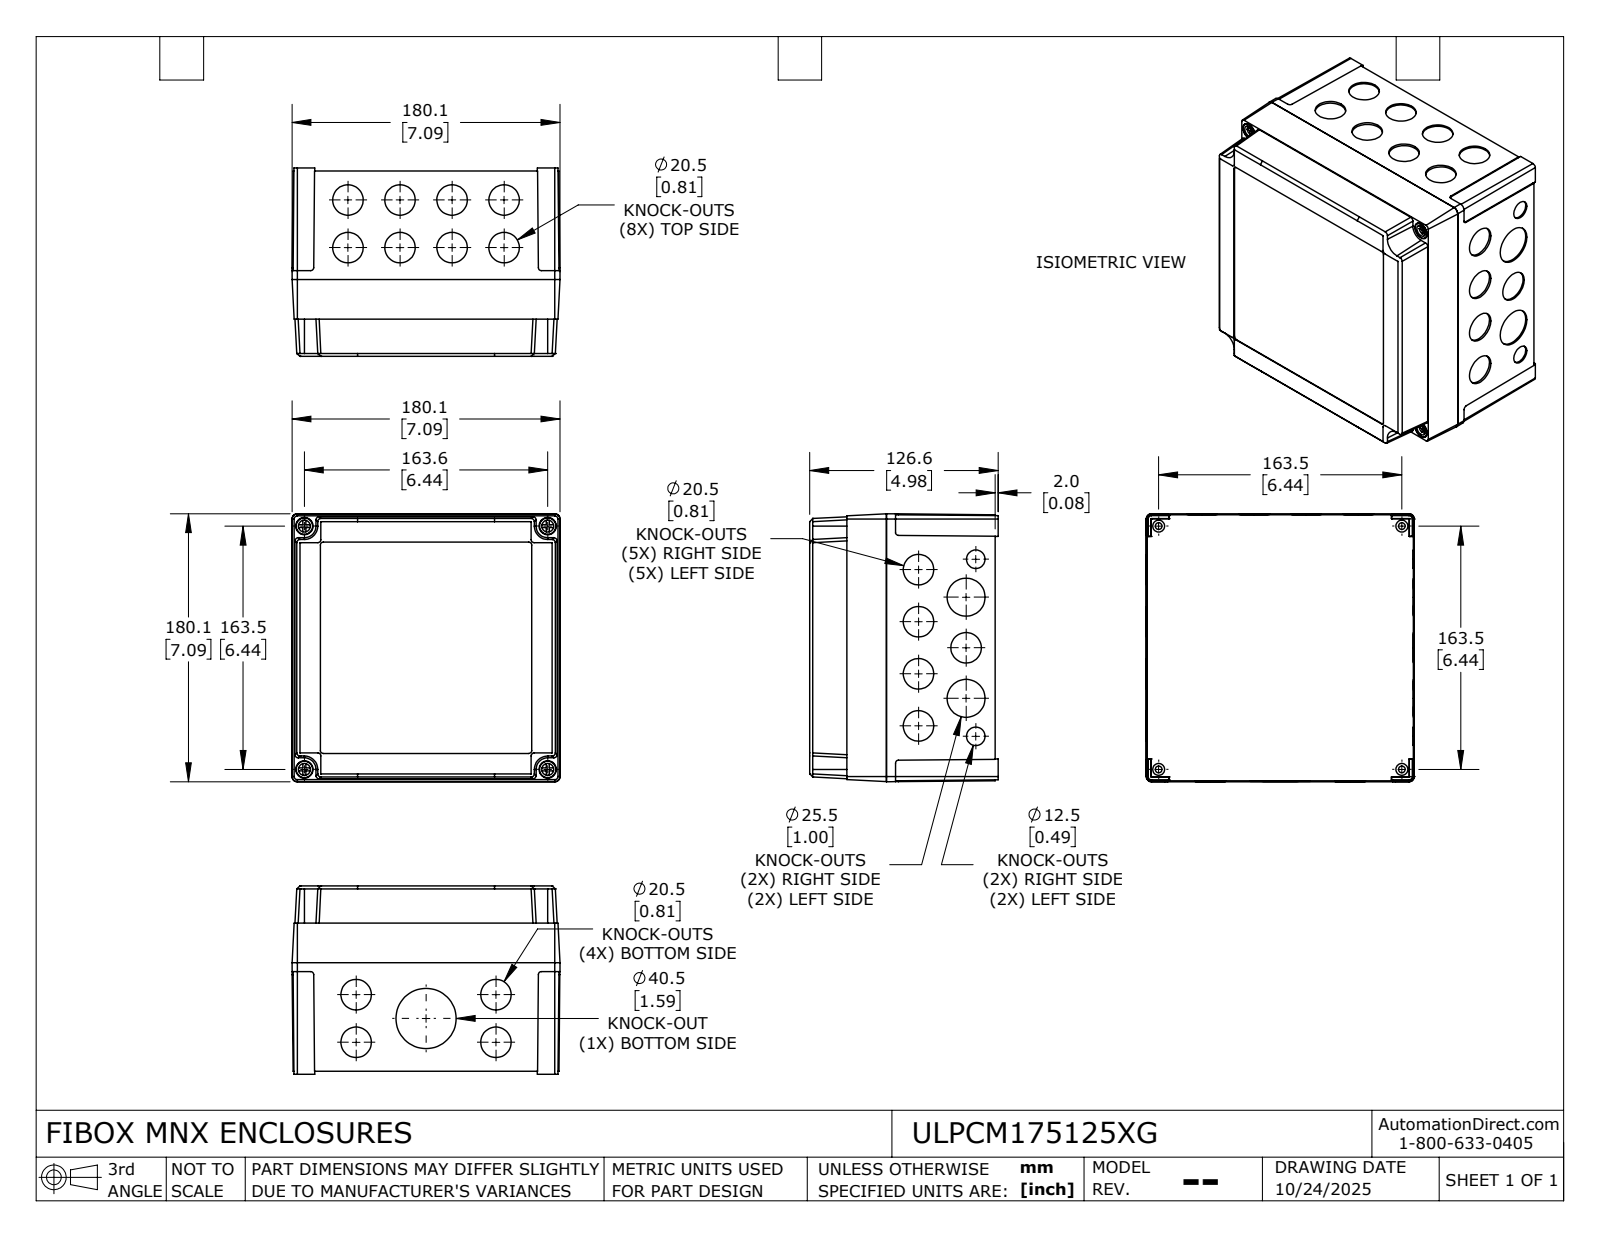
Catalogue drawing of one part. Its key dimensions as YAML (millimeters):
part_name: "ULPCM175125XG"
step_written_by: "SolidWorks 2024 (AUTOMOTIVE_DESIGN)"
units: millimeters
bodies: {solids: 12, faces: 544, planar: 358, cylindrical: 136, other: 50}
overall_size: [180.1, 180.1, 126.6]
volume: 474625
surface_area: 316260
round_holes:
  - {diameter: 20.5, count: 17}
  - {diameter: 3.2, count: 12}
  - {diameter: 4, count: 12}
  - {diameter: 8, count: 8}
  - {diameter: 4.5, count: 4}
  - {diameter: 11.6, count: 4}
  - {diameter: 12.5, count: 2}
  - {diameter: 25.5, count: 2}
  - {diameter: 40.5, count: 1}
round_bosses_or_shafts:
  - {diameter: 8, count: 12}
  - {diameter: 2.5, count: 8}
  - {diameter: 11, count: 4}
  - {diameter: 7.2, count: 4}
partial_cylinders:
  - {radius: 2, count: 8}
  - {radius: 2.1, count: 8}
  - {radius: 5, count: 4}
face_to_face_distances: [4.2, 122.1, 3, 119.1, 2, 124.1, 121.1, 1.96, 1.4, 0.56]
hole_center_spacings: [163.5, 35, 33.85, 50, 72.8, 82.59, 121.66, 132.27]
